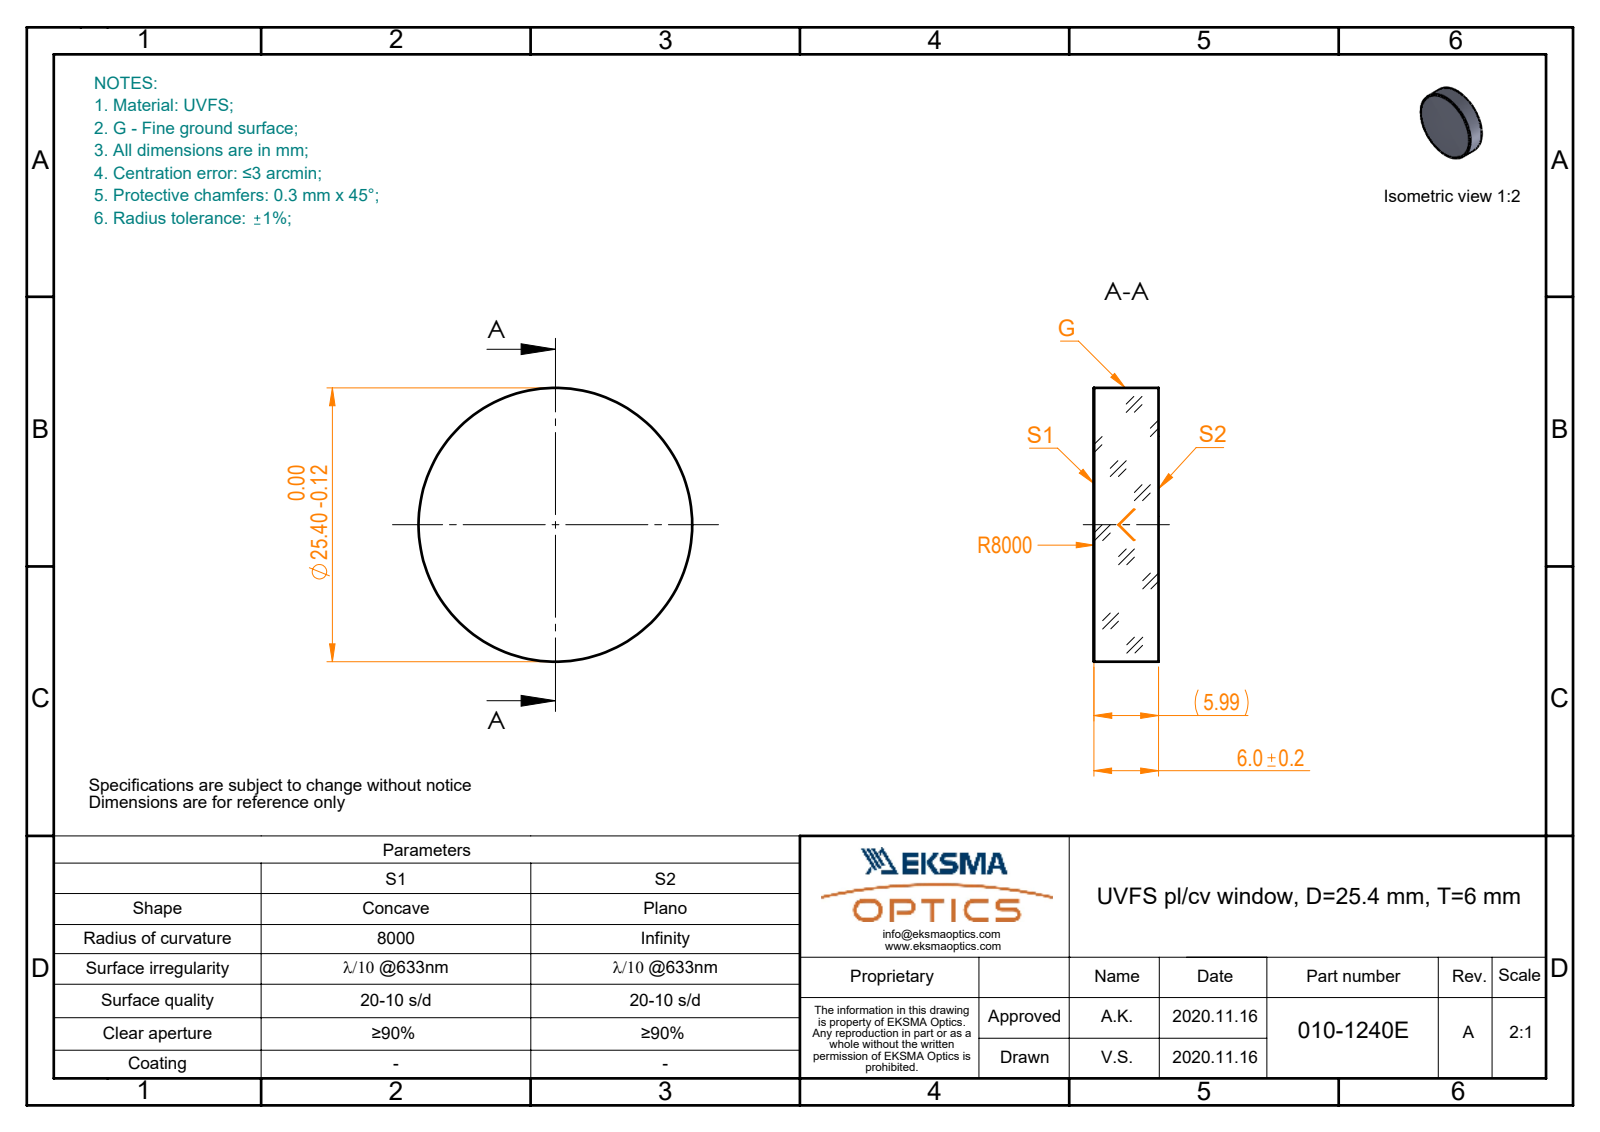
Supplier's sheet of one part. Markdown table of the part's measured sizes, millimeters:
| quantity | value |
| --- | --- |
| part name | 010-1240E_UVFS_PCV_window |
| STEP written by | SolidWorks 2019 (CONFIG_CONTROL_DESIGN) |
| units | millimeters |
| bodies | 1 solid, 5 faces (1 planar, 2 cylindrical, 2 other) |
| overall size | 25.4 × 25.4 × 6 |
| volume | 3 038 mm³ |
| surface area | 1 492 mm² |
| round bosses / shafts (diameter × count) | 25.4 × 1 |
